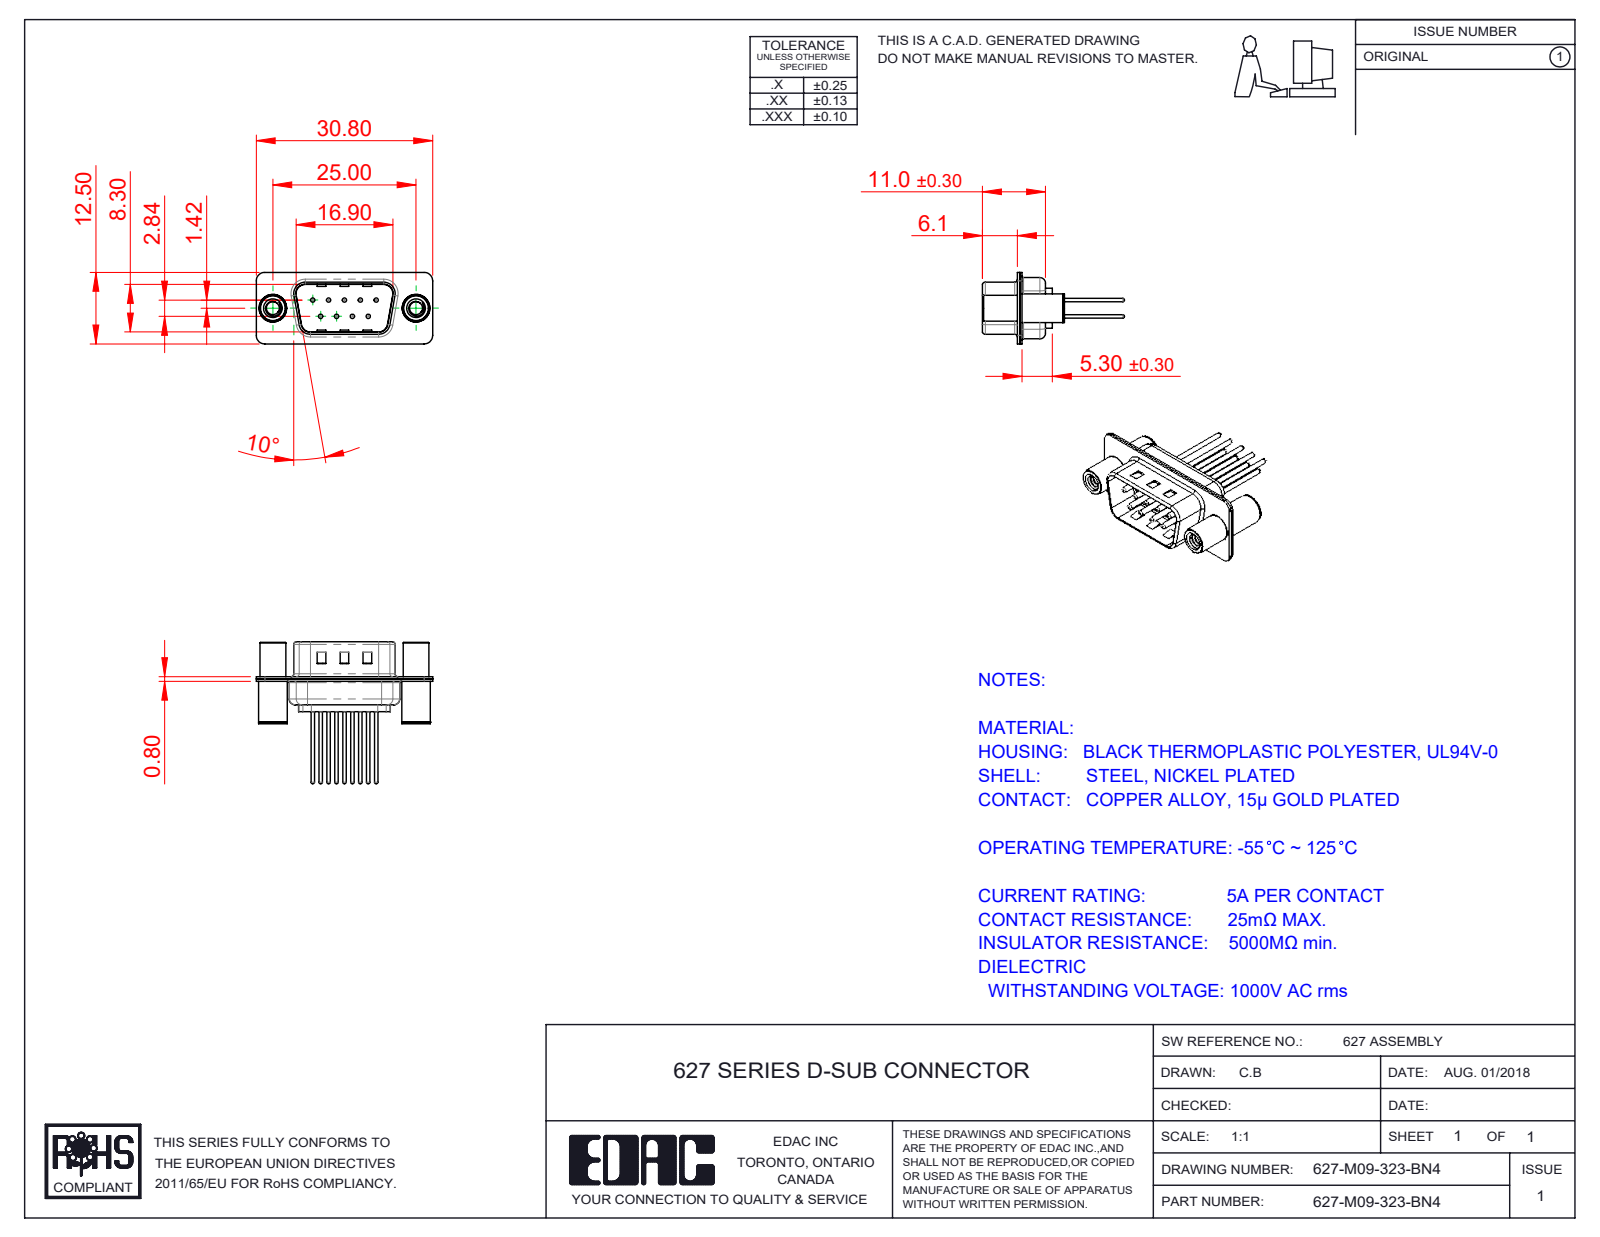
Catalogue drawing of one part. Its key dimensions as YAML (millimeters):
part_name: "627M Housing_09 Contacts; 627M Contact Row 1_23; 627M 4-40 Threaded Standoff and Board Spacer; 627M Shell Front_09 Contacts (+3 more)"
step_written_by: "SolidWorks 2020 (CONFIG_CONTROL_DESIGN)"
units: millimeters
bodies: {solids: 14, faces: 723, planar: 176, cylindrical: 307, other: 240}
overall_size: [30.8, 24.77, 12.5]
volume: 1615
surface_area: 4220
round_holes:
  - {diameter: 0.75, count: 9}
  - {diameter: 1.6, count: 9}
  - {diameter: 2, count: 9}
  - {diameter: 2.26, count: 2}
  - {diameter: 3.26, count: 2}
  - {diameter: 4, count: 2}
  - {diameter: 4.8, count: 2}
round_bosses_or_shafts:
  - {diameter: 1.5, count: 9}
  - {diameter: 0.6, count: 9}
  - {diameter: 5, count: 2}
  - {diameter: 4.9, count: 2}
  - {diameter: 4.5, count: 2}
partial_cylinders:
  - {radius: 1.5, count: 16}
  - {radius: 2, count: 12}
  - {radius: 0.5, count: 8}
  - {radius: 1.6, count: 8}
  - {radius: 0.25, count: 4}
  - {radius: 0.6, count: 4}
  - {radius: 0.65, count: 4}
  - {radius: 0.9, count: 4}
face_to_face_distances: [0.4, 0.8, 9.5, 9.1, 8.7, 0.65, 9.9, 1.2, 5.3, 6.1]
hole_center_spacings: [3.16, 2.77, 5.54, 5.03, 5.04, 8.31, 7.1, 7.48]
